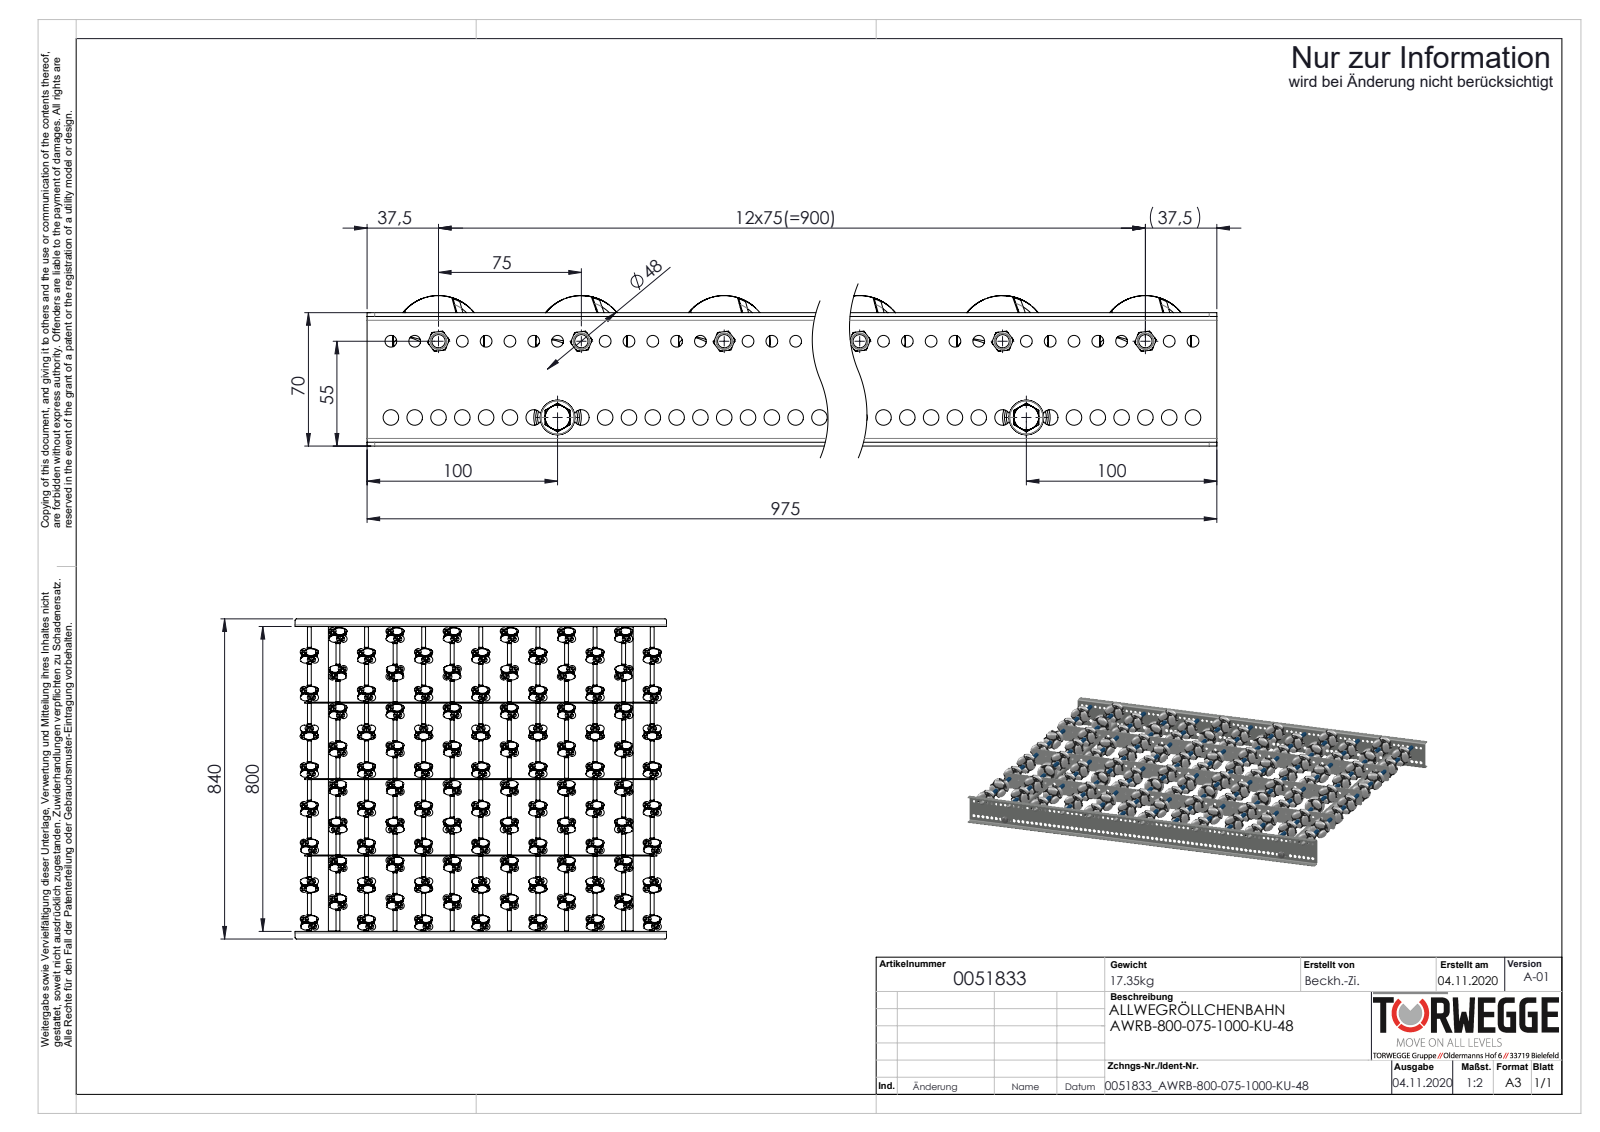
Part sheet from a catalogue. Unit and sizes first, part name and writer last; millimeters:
Units: millimetres
Overall size (bounding box): 975 × 840 × 79
Round holes (diameter × count): ⌀3.7 ×624, ⌀4.2 ×624, ⌀6.2 ×77, ⌀8.2 ×77, ⌀6.5 ×37, ⌀4.92 ×13, ⌀8.4 ×13, ⌀6.8 ×2, ⌀21 ×2
Round bosses / shafts (diameter × count): ⌀4 ×624, ⌀3.7 ×543, ⌀8 ×15, ⌀47.1 ×13, ⌀42 ×13, ⌀11 ×13, ⌀10 ×13, ⌀7 ×13
Partial cylindrical surfaces — rounded edges, fillets, slot ends (radius × count): R4 ×8, R2 ×4, R5 ×4
Main face-to-face distances: 2, 200.5, 2.5, 802, 401, 203, 198, 68, 800, 804
Hole centre spacings: 36.06, 36.05, 99, 36.07, 36.04, 150, 75, 122.72
Volume: 5 898 000 mm³ · Surface area: 4 023 000 mm²
Bodies: 1718 solids, 30294 faces (10564 planar, 11852 cylindrical, 7878 other)
Part name (STEP PRODUCT): AWR-Achse-für-Konfiguration_L800; S108767_Längstraverse-42x2,5-AWR_L975; 0027528_BUCHSE-HOHLNIETE ZU AWR48; 0015028_AWR48 (+8 more)
STEP written by: SolidWorks 2020 (AUTOMOTIVE_DESIGN)
